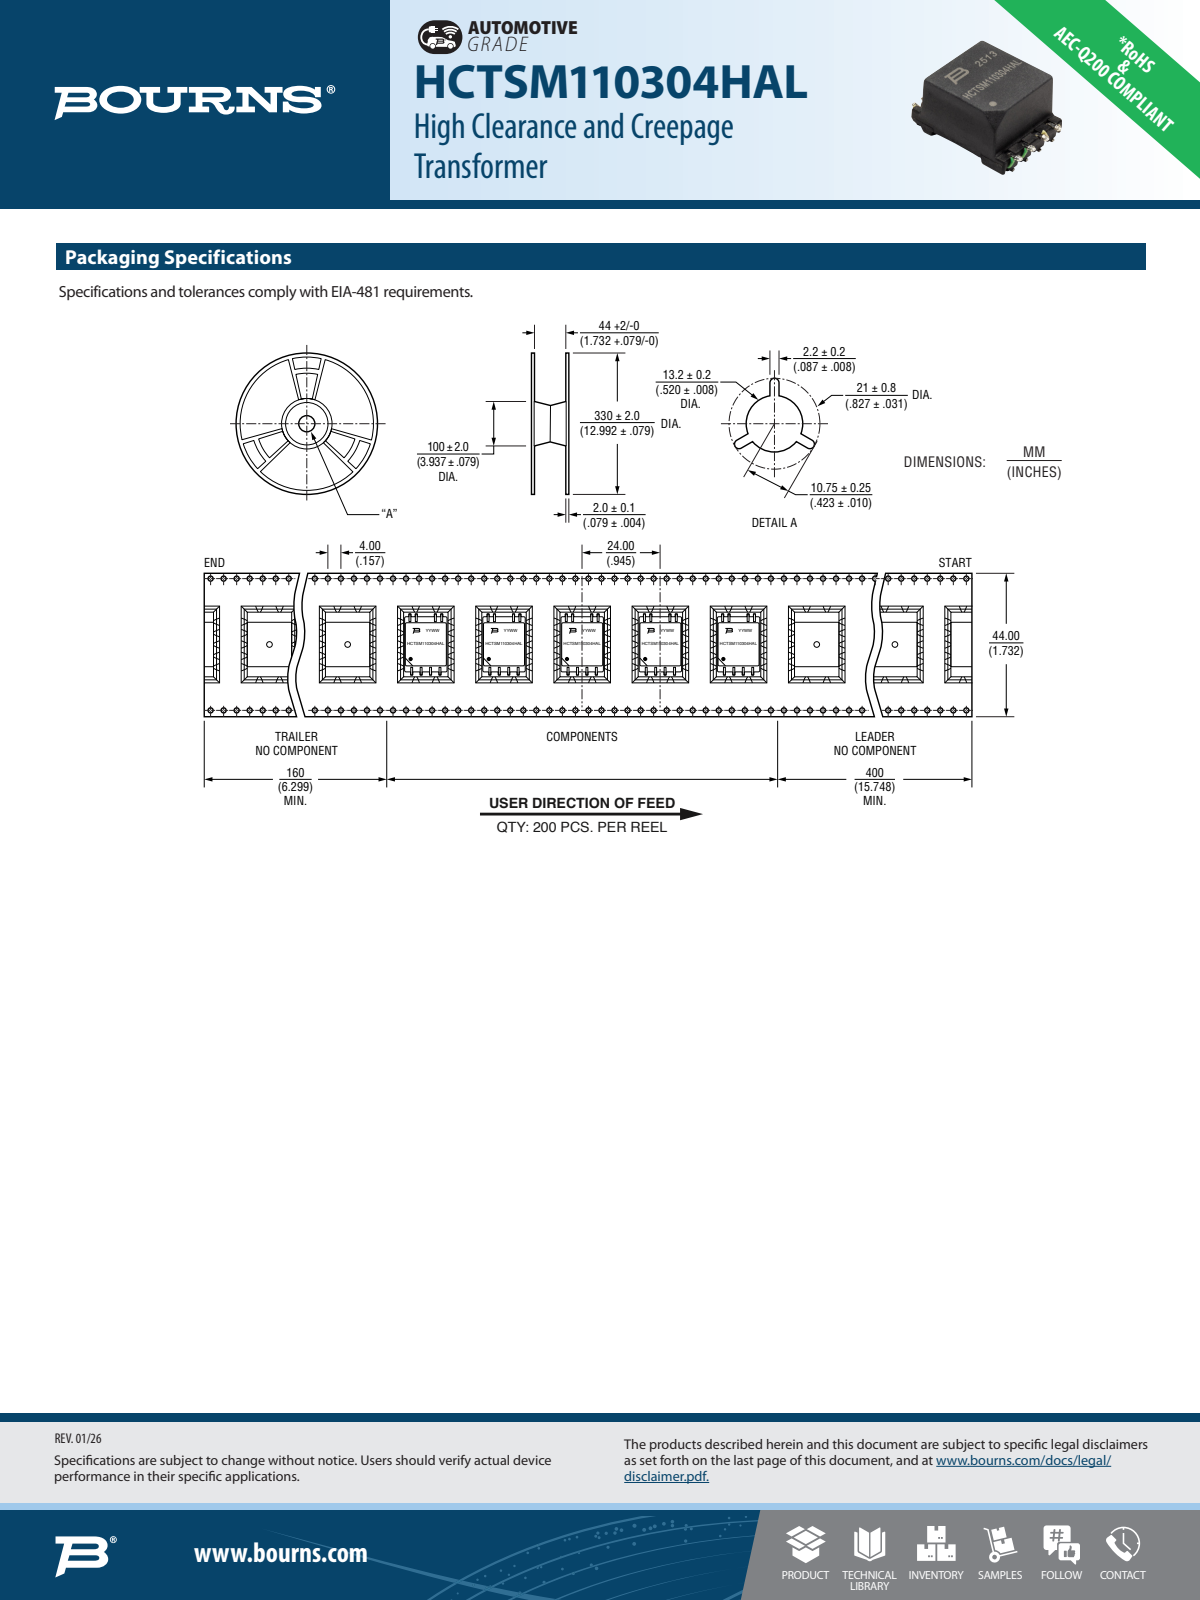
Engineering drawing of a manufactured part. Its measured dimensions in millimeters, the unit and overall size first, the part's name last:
Units: millimetres
Overall size (bounding box): 19.6 × 13.5 × 9.6
Round holes (diameter × count): ⌀1.35 ×1, ⌀1.8 ×1
Partial cylindrical surfaces — rounded edges, fillets, slot ends (radius × count): R0.15 ×67, R0.3 ×51, R0.2 ×16, R0.8 ×11, R1 ×10, R0.5 ×6, R0.7 ×6, R0.4 ×4
Main face-to-face distances: 8.3, 1, 9.3, 0.8, 1.5, 1.1, 6.1, 6.05, 0.7, 17.4
Hole centre spacings: 2.64
Volume: 1 645 mm³ · Surface area: 1 091 mm²
Bodies: 1 solid, 1103 faces (683 planar, 238 cylindrical, 182 other)
Part name (STEP PRODUCT): H1520-CASE
STEP written by: PRO/ENGINEER BY PARAMETRIC TECHNOLOGY CORPORATION, 2001280 (CONFIG_CONTROL_DESIGN)
